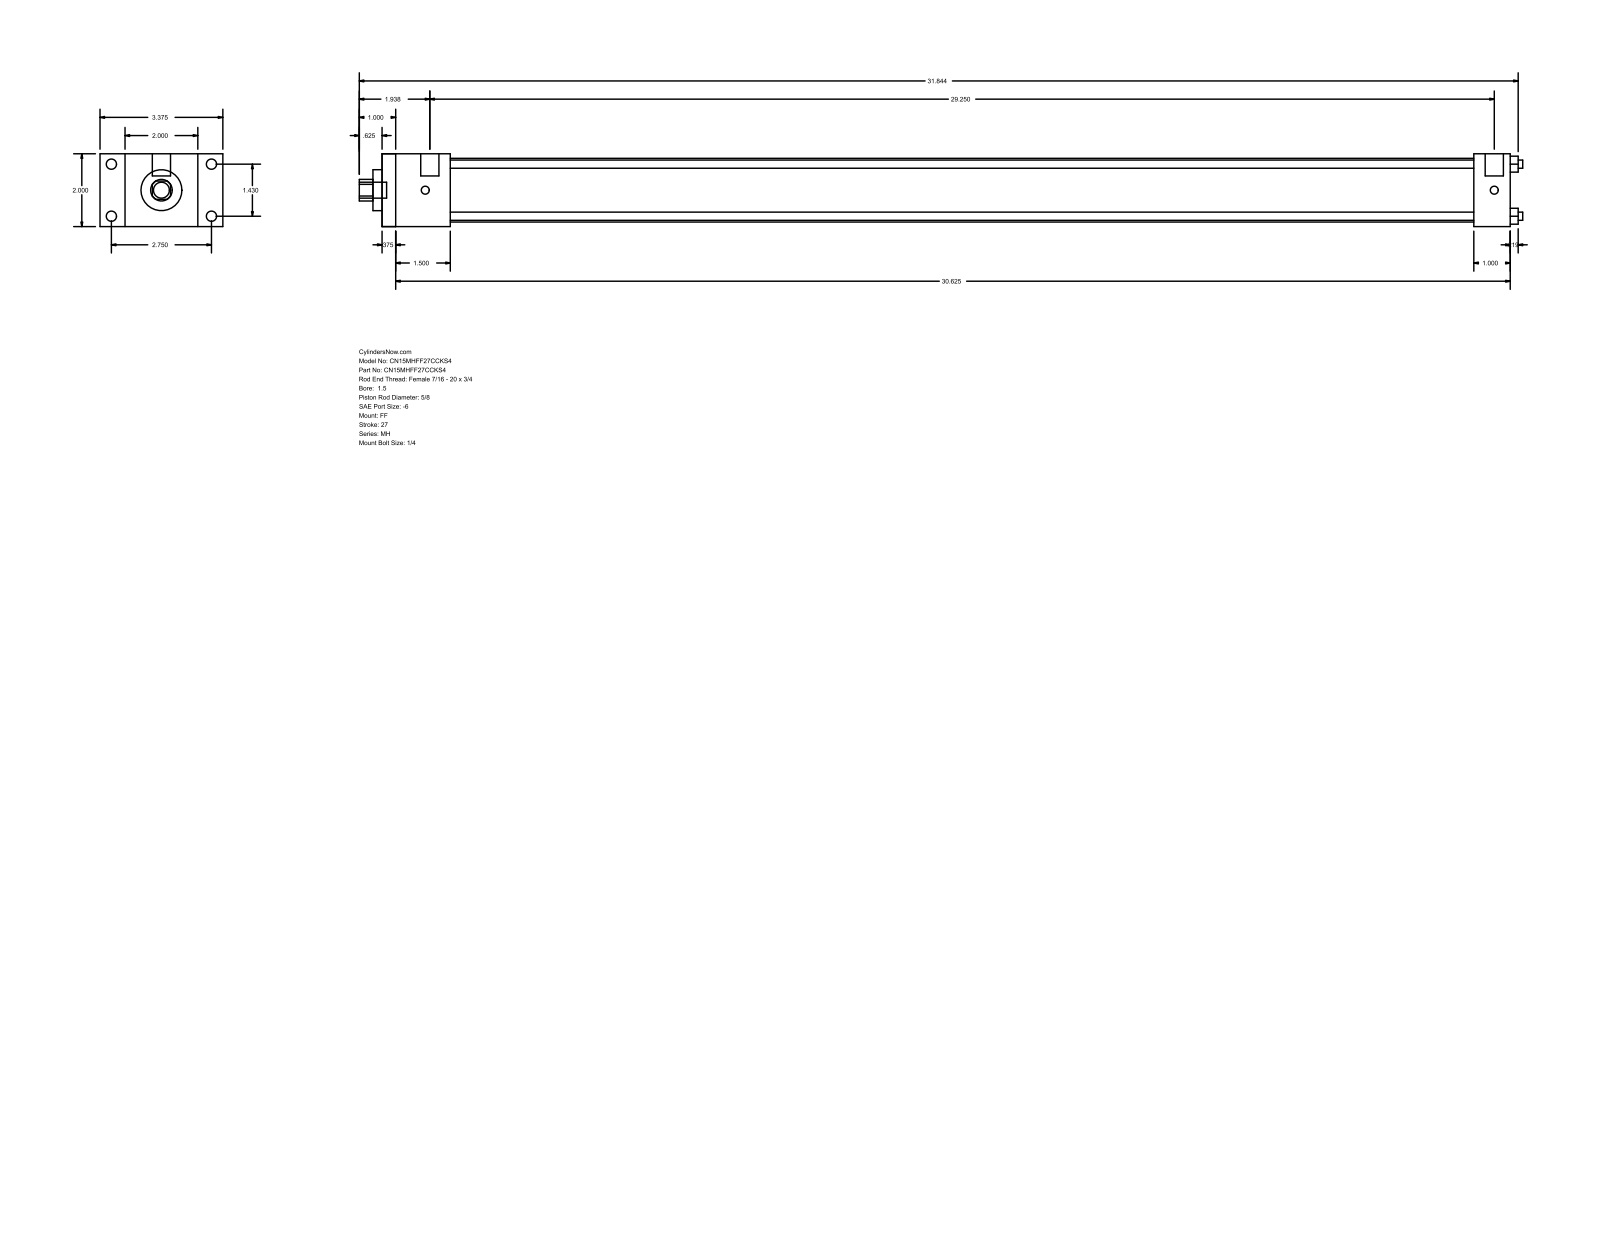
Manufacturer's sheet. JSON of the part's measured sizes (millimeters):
{"part_name": "MH_FF__0150_0.625", "step_written_by": "GSSL Pune (CONFIG_CONTROL_DESIGN)", "units": "millimeters", "bodies": {"solids": 0, "faces": 92, "planar": 64, "cylindrical": 28, "other": 0}, "overall_size": [812.01, 85.72, 50.8], "round_holes": [[5.71, 4], [15.88, 1], [28.57, 1], [44.45, 1]], "round_bosses_or_shafts": [[7.14, 4], [5.56, 4], [12.7, 2], [11.11, 1]], "partial_cylinders_radius": [[7.54, 1]], "face_to_face_distances": [50.8, 787.39, 9.52, 777.87, 17.46, 68.26, 47.62, 38.1, 739.77, 762], "hole_center_spacings": [25.68, 36.32, 51.36]}
